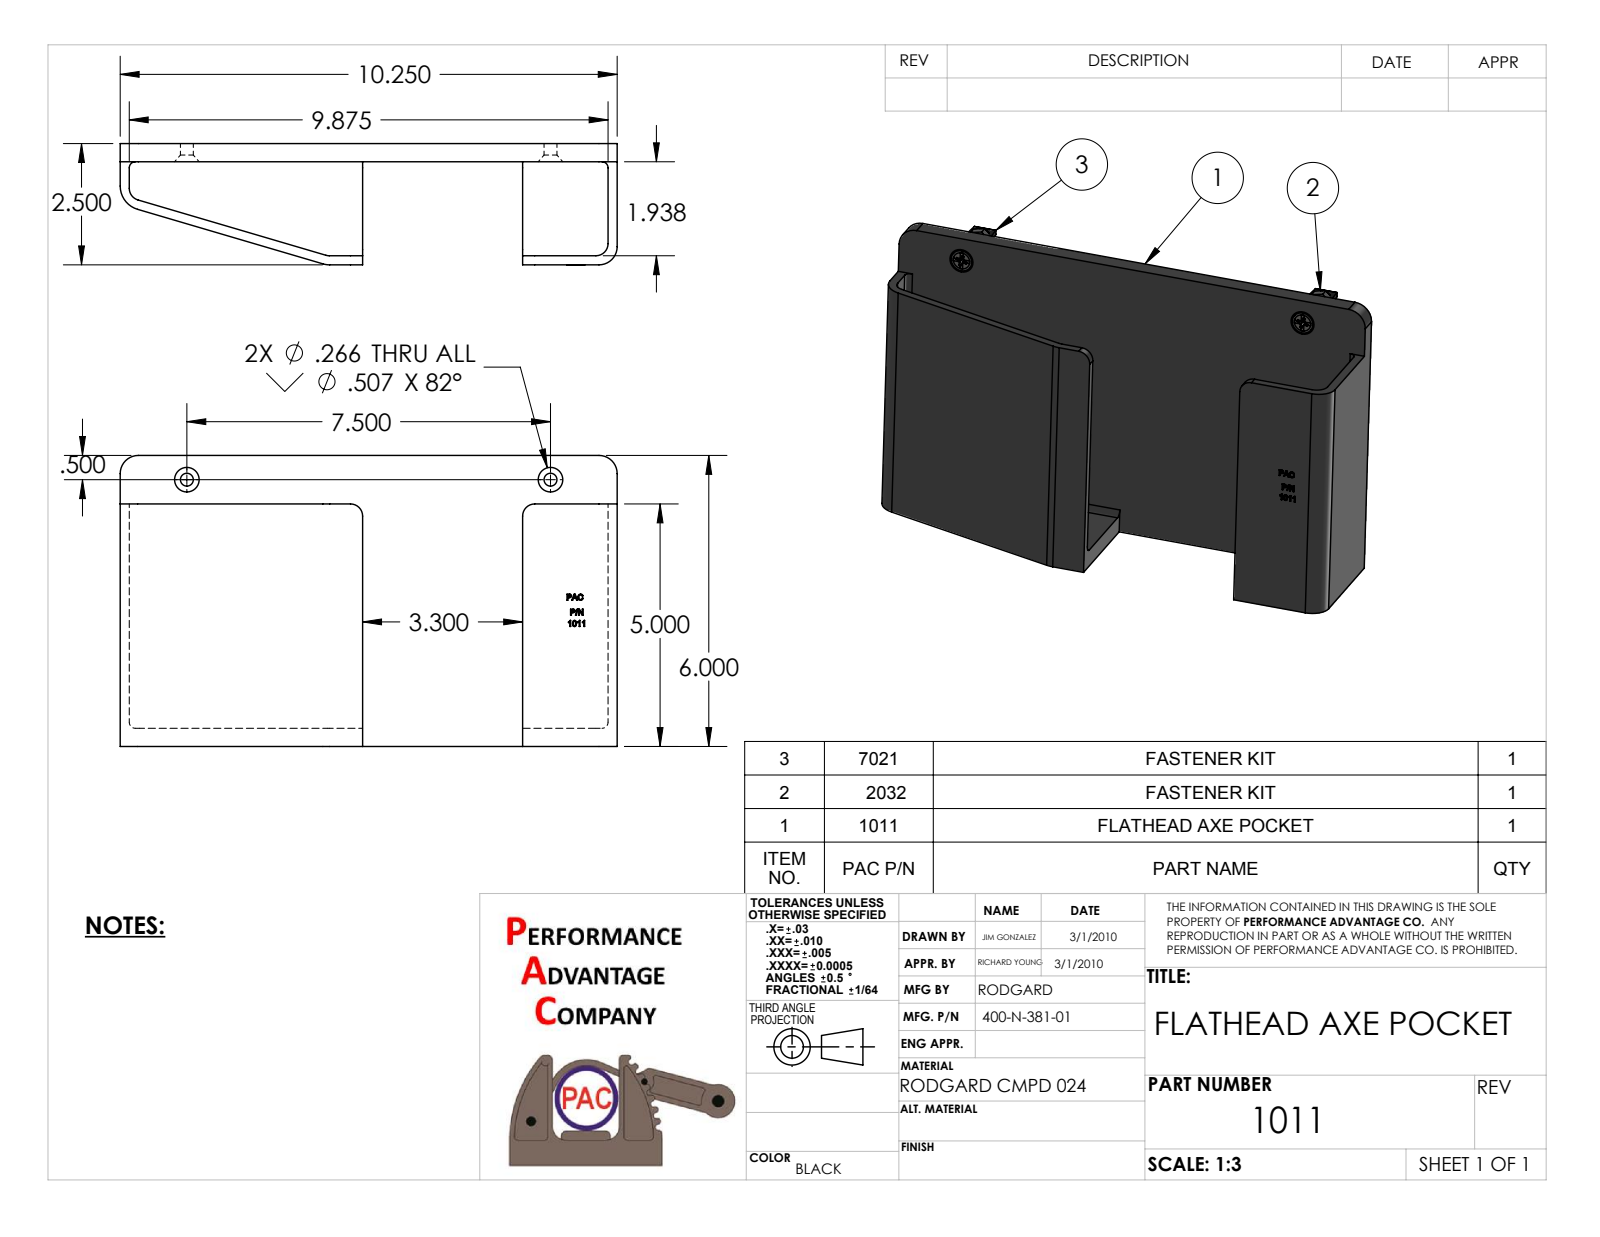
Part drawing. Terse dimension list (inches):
name: 1011
written by: SolidWorks 2010 (CONFIG_CONTROL_DESIGN)
unit: in
bodies: 1 solid, 162 faces (92 planar, 23 cylindrical, 47 other)
size: 10.25 × 6 × 2.505
volume: 35.89 in³; area: 249.1 in²
holes: 2× ⌀0.266
rounds: 7× R0.125, 5× R0.25, 3× R0.375, 2× R0.5
face distances: 0.375, 0.188, 2.125, 2.5, 0.187, 1.938, 2.313, 0.375, 10.062, 10.25
hole spacings: 7.5
